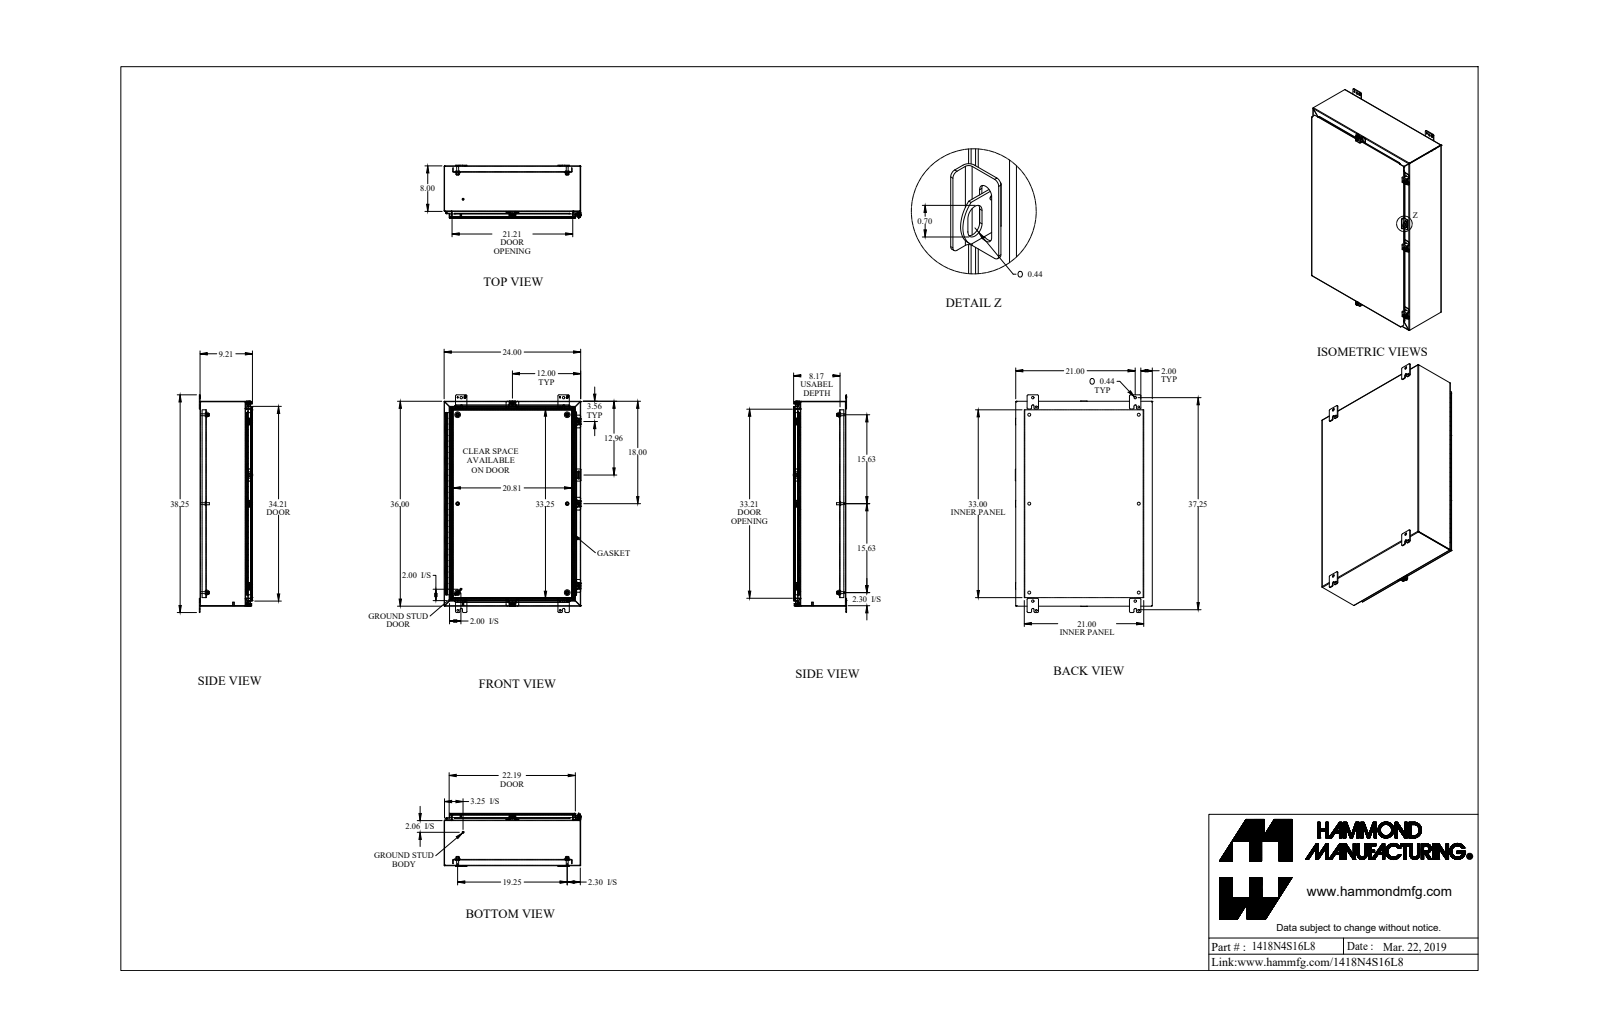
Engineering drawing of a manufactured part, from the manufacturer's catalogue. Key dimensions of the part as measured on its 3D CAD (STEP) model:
Part name (STEP PRODUCT): 1418N4S16L8_Default
STEP written by: SolidWorks 2019 (CONFIG_CONTROL_DESIGN)
Units: inches
Bodies: 49 solids, 1661 faces (876 planar, 633 cylindrical, 152 other)
Overall size (bounding box): 38.25 × 24.063 × 9.375
Volume: 302.5 in³ · Surface area: 7 920 in²
Round holes (diameter × count): ⌀0.5 ×6, ⌀0.213 ×5, ⌀0.265 ×5, ⌀0.375 ×5, ⌀0.307 ×4, ⌀0.313 ×4, ⌀0.437 ×4, ⌀0.445 ×4, ⌀0.11 ×1, ⌀0.125 ×1
Round bosses / shafts (diameter × count): ⌀0.65 ×6, ⌀0.375 ×6, ⌀0.332 ×6, ⌀0.5 ×5, ⌀0.39 ×5, ⌀0.244 ×5, ⌀1 ×4, ⌀0.313 ×2
Partial cylindrical surfaces — rounded edges, fillets, slot ends (radius × count): R0.048 ×27, R0.143 ×27, R0.188 ×26, R0.036 ×24, R0.108 ×24, R0.25 ×24, R0.125 ×12, R0.141 ×10
Main face-to-face distances: 0.072, 0.072, 9.066, 9.138, 9.138, 0.937, 9.21, 0.095, 1.009, 8.106
Hole centre spacings: 15.625, 19.25, 34.735, 9.857, 31.25, 36.703, 15.769, 18
